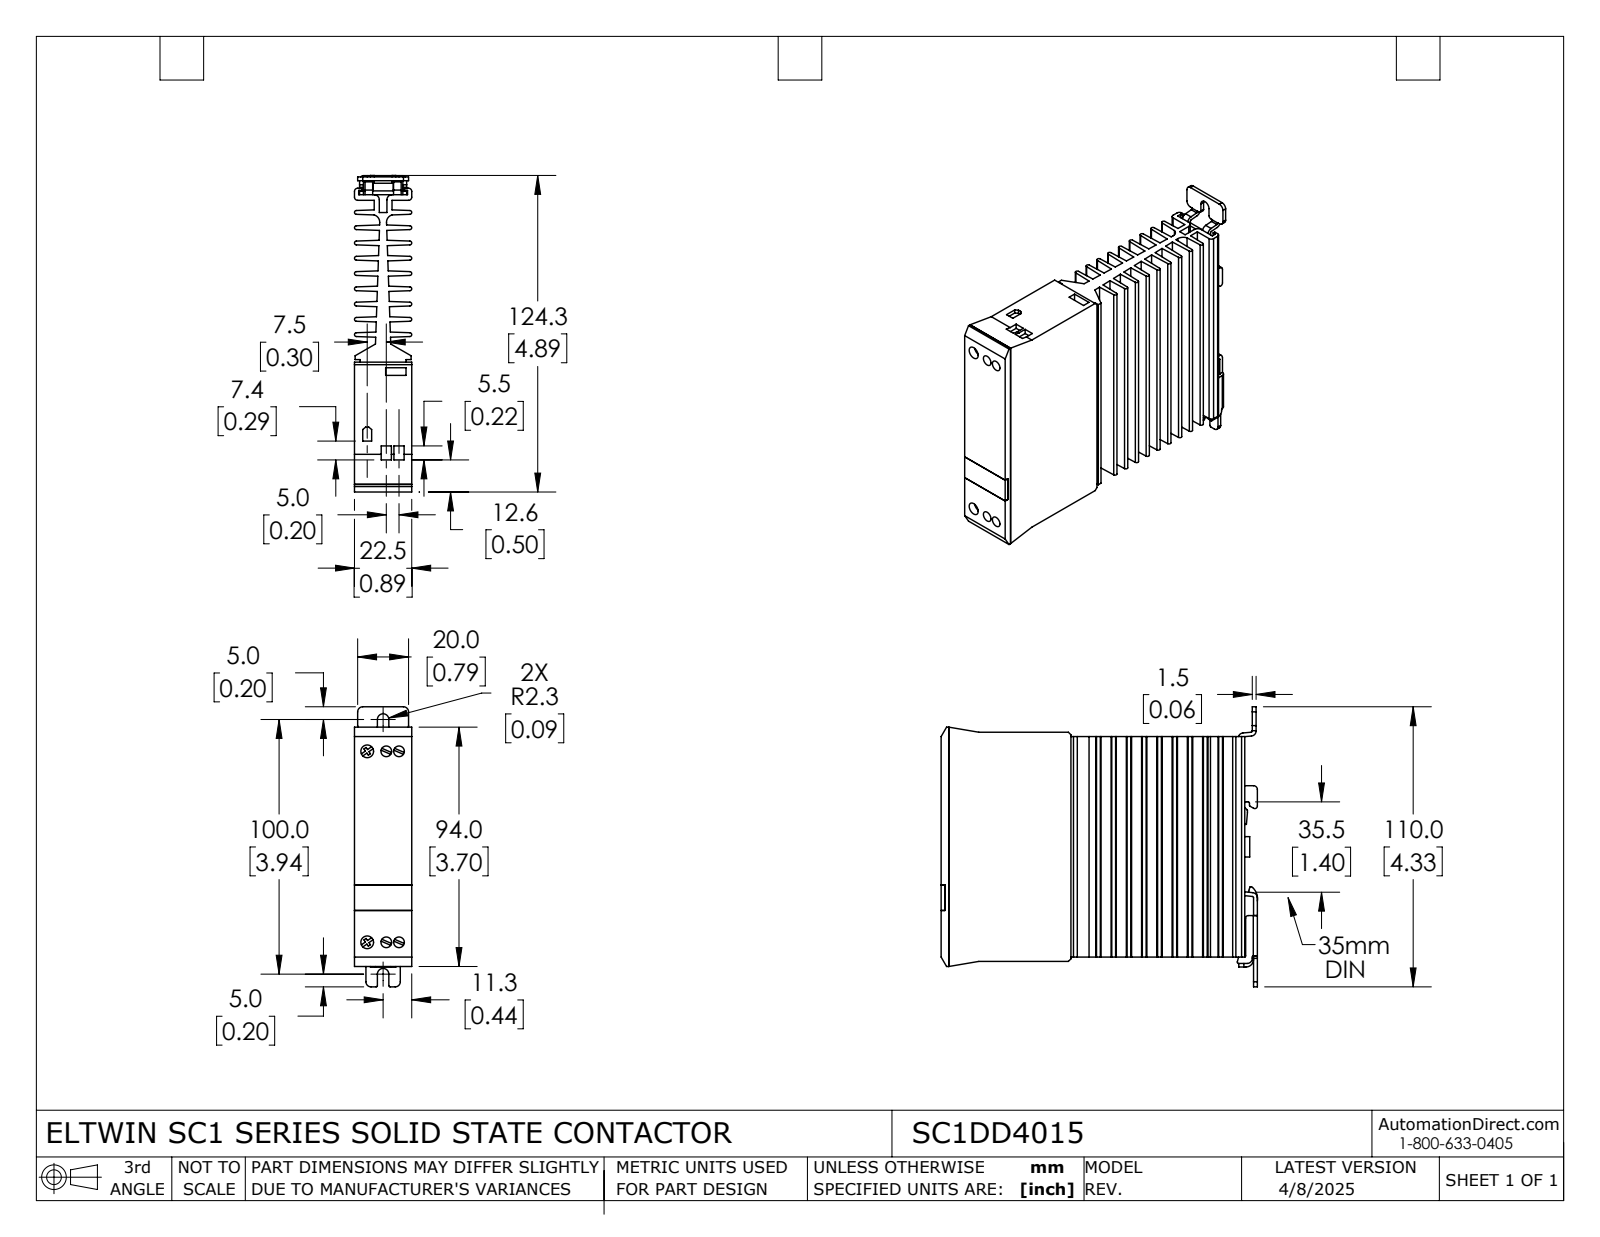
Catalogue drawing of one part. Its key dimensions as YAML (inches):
part_name: "SC1DD4015"
step_written_by: "SolidWorks 2021 (AUTOMOTIVE_DESIGN)"
units: inches
bodies: {solids: 6, faces: 489, planar: 326, cylindrical: 161, other: 2}
overall_size: [4.894, 4.331, 0.886]
volume: 10.14
surface_area: 115.4
round_holes:
  - {diameter: 0.165, count: 4}
  - {diameter: 0.173, count: 4}
  - {diameter: 0.197, count: 2}
  - {diameter: 0.236, count: 2}
round_bosses_or_shafts:
  - {diameter: 0.315, count: 1}
partial_cylinders:
  - {radius: 0.02, count: 29}
  - {radius: 0.03, count: 18}
  - {radius: 0.079, count: 18}
  - {radius: 0.039, count: 15}
  - {radius: 0.059, count: 5}
  - {radius: 0.049, count: 4}
  - {radius: 0.118, count: 3}
  - {radius: 0.004, count: 2}
face_to_face_distances: [0.236, 0.472, 0.708, 0.148, 0.56, 0.236, 1.18, 0.088, 0.62, 0.324]
hole_center_spacings: [2.953, 0.197, 0.295, 0.492, 2.959, 2.967, 2.993]
